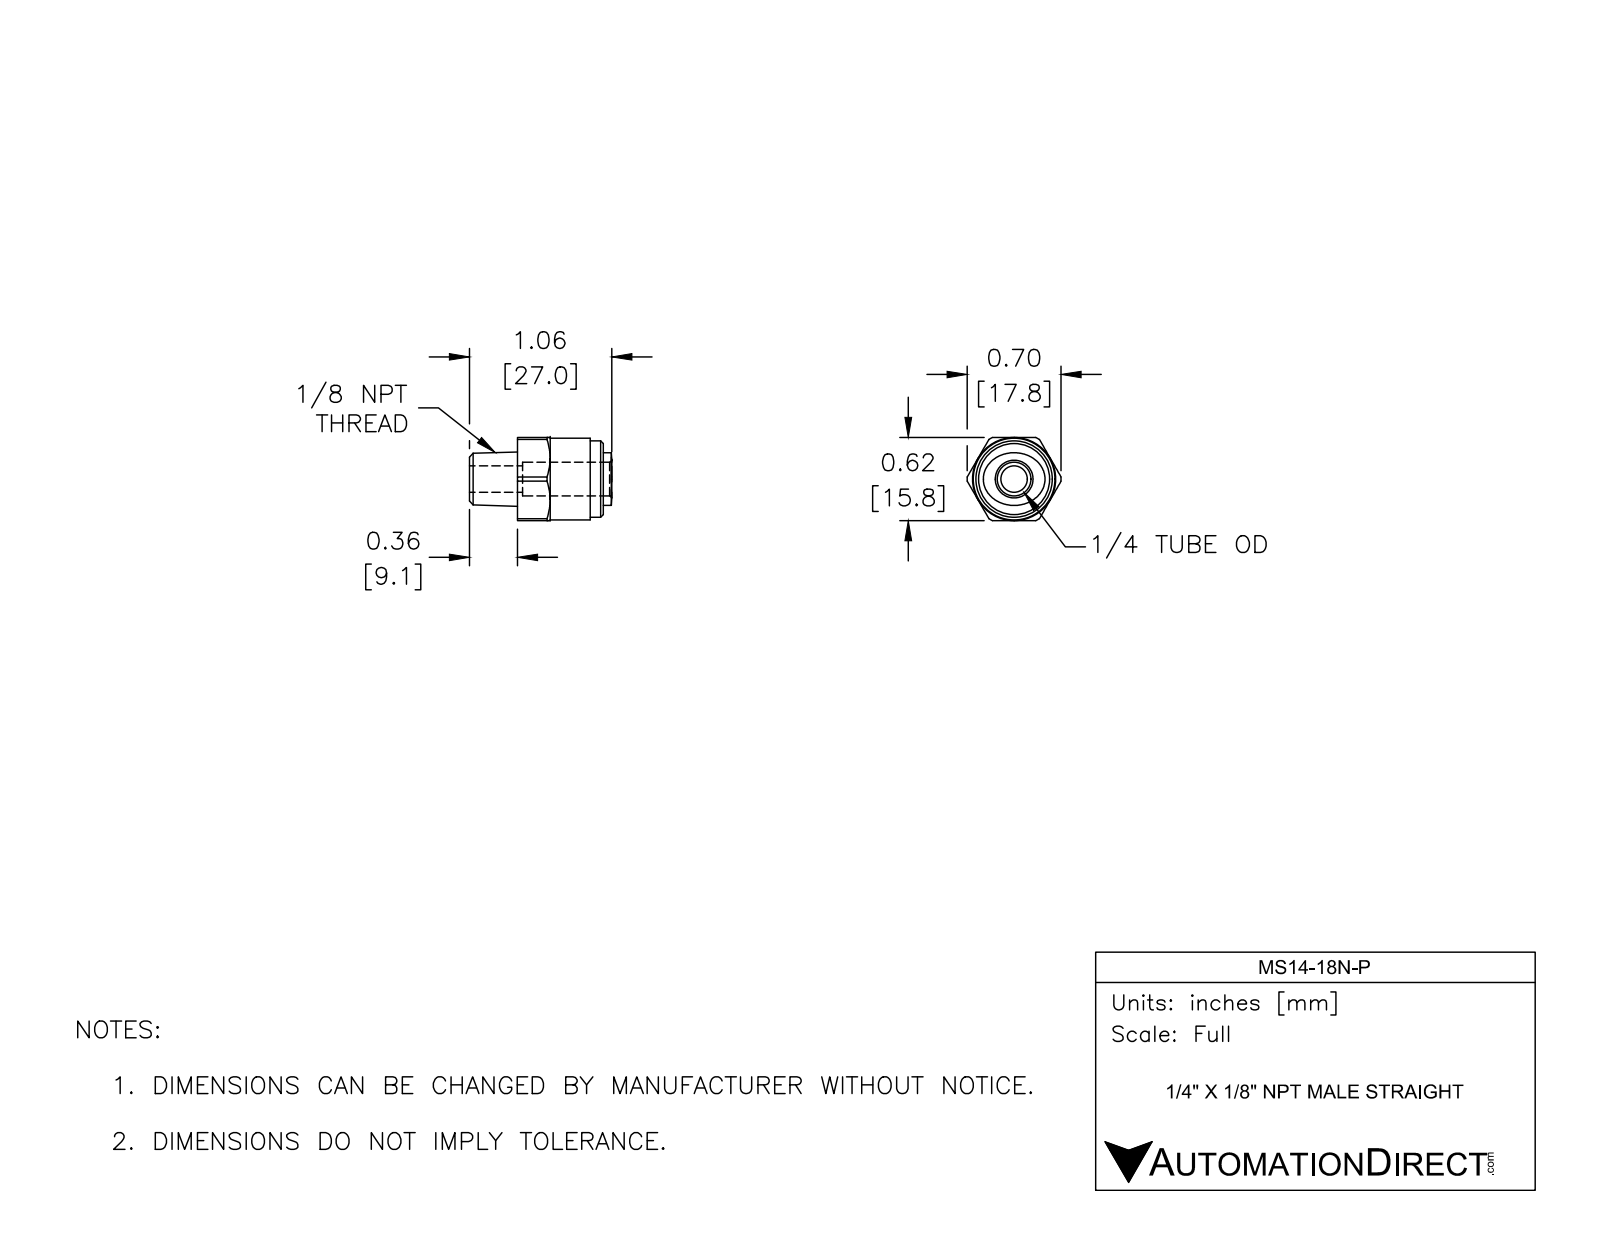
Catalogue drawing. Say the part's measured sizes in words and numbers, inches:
The part is named "MS14-18N-P". Its 3-D file was written by "SolidWorks 2017 (AUTOMOTIVE_DESIGN)". It is 1 solid with 46 faces: 12 planar, 15 cylindrical and 19 other. Overall it measures 1.063 by 0.701 by 0.622 inches. Its volume is 0.201 cubic inches and its surface area 3.093 square inches. Round holes: 1 of diameter 0.197, 1 of diameter 0.25. Round bosses or shafts: 1 of diameter 0.61, 1 of diameter 0.571. Partial cylindrical surfaces (rounded edges, fillets, slot ends): 1 of radius 0.35. The main face-to-face distances are 0.622, 0.642, 0.358, 1, 0.902, 0.543, 0.098, 0.398, 0.602, 0.039.
